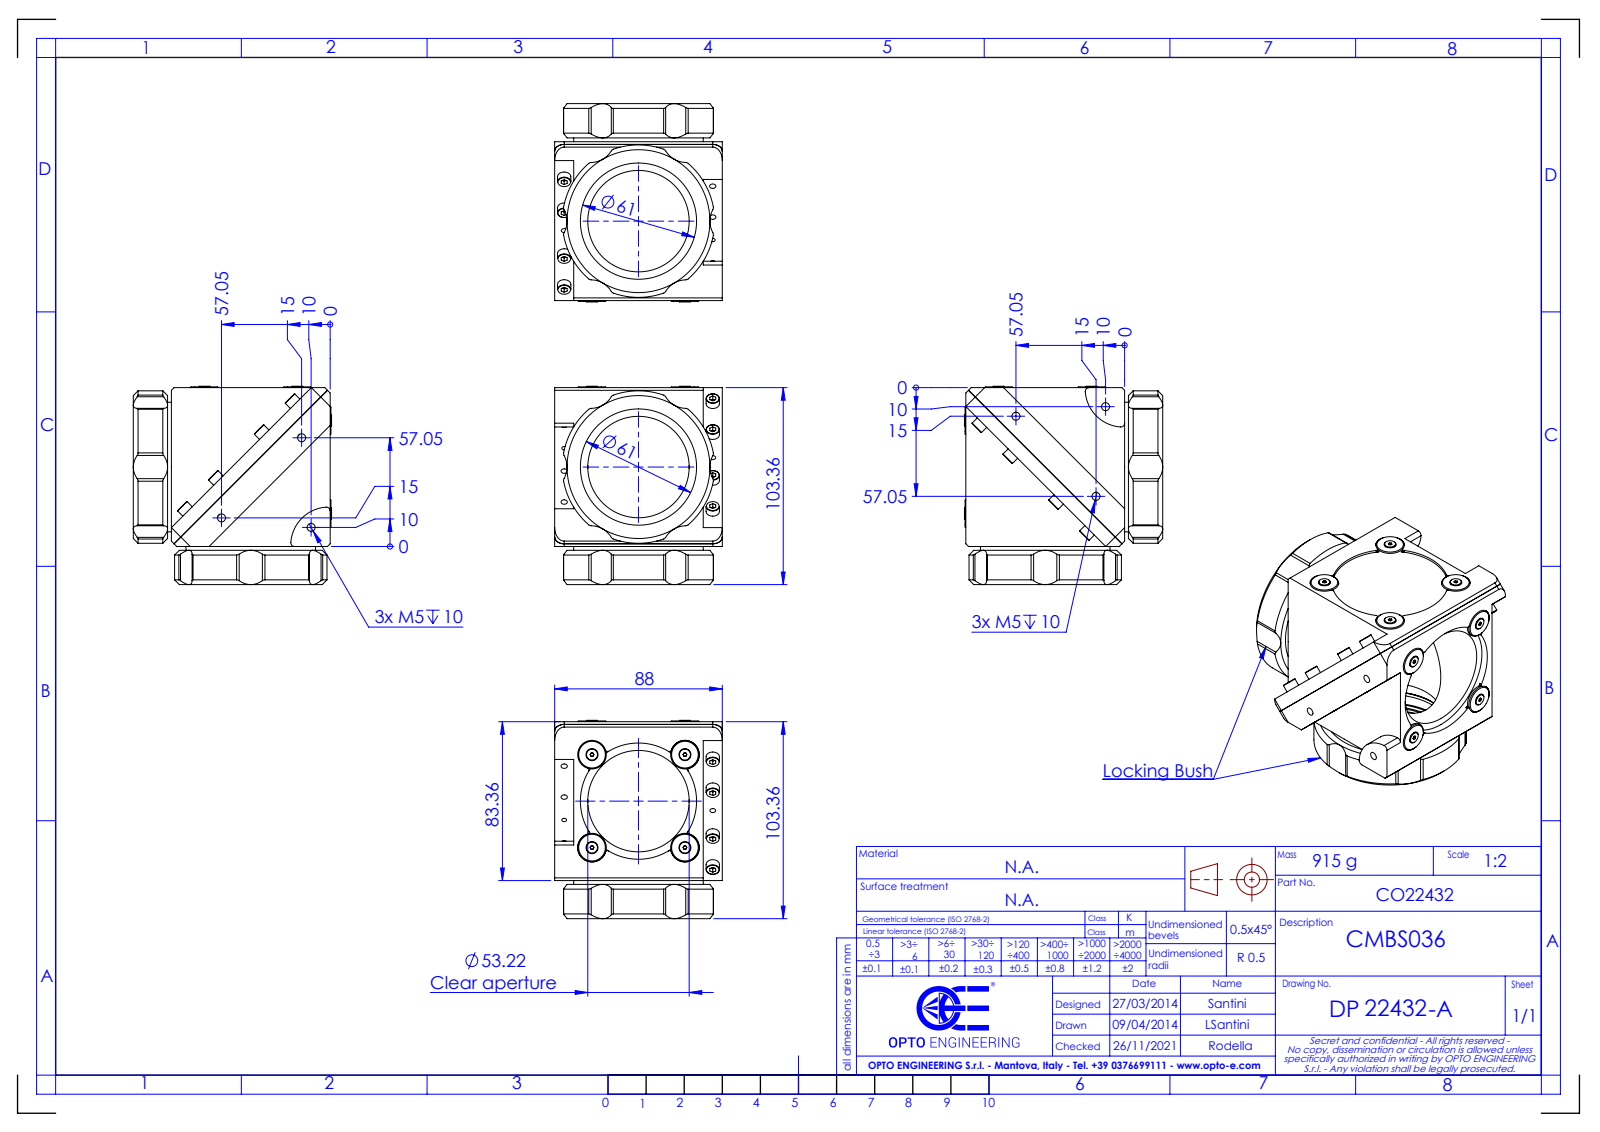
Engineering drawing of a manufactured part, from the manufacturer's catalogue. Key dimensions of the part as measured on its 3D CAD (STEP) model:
Part name (STEP PRODUCT): DP22432 -A_CMBS036
STEP written by: SolidWorks 2021 (CONFIG_CONTROL_DESIGN)
Units: millimetres
Bodies: 0 solids, 517 faces (169 planar, 232 cylindrical, 116 other)
Overall size (bounding box): 104.09 × 104.09 × 88
Round holes (diameter × count): ⌀3.3 ×8, ⌀4.2 ×6, ⌀15 ×4, ⌀2.5 ×2, ⌀3 ×2, ⌀53.22 ×2, ⌀61 ×2, ⌀61.6 ×2, ⌀63.2 ×2, ⌀65 ×2
Round bosses / shafts (diameter × count): ⌀7 ×8, ⌀5.75 ×8, ⌀15 ×4, ⌀68 ×2
Partial cylindrical surfaces — rounded edges, fillets, slot ends (radius × count): R2 ×28, R1 ×16, R12.5 ×12, R5 ×4, R25 ×4, R20 ×2, R40 ×2
Main face-to-face distances: 2, 78, 10, 83.36, 68, 7, 79.36, 3, 4, 20
Hole centre spacings: 78, 17, 22.95, 34.51, 39.95, 47.31, 56.95, 60.6
